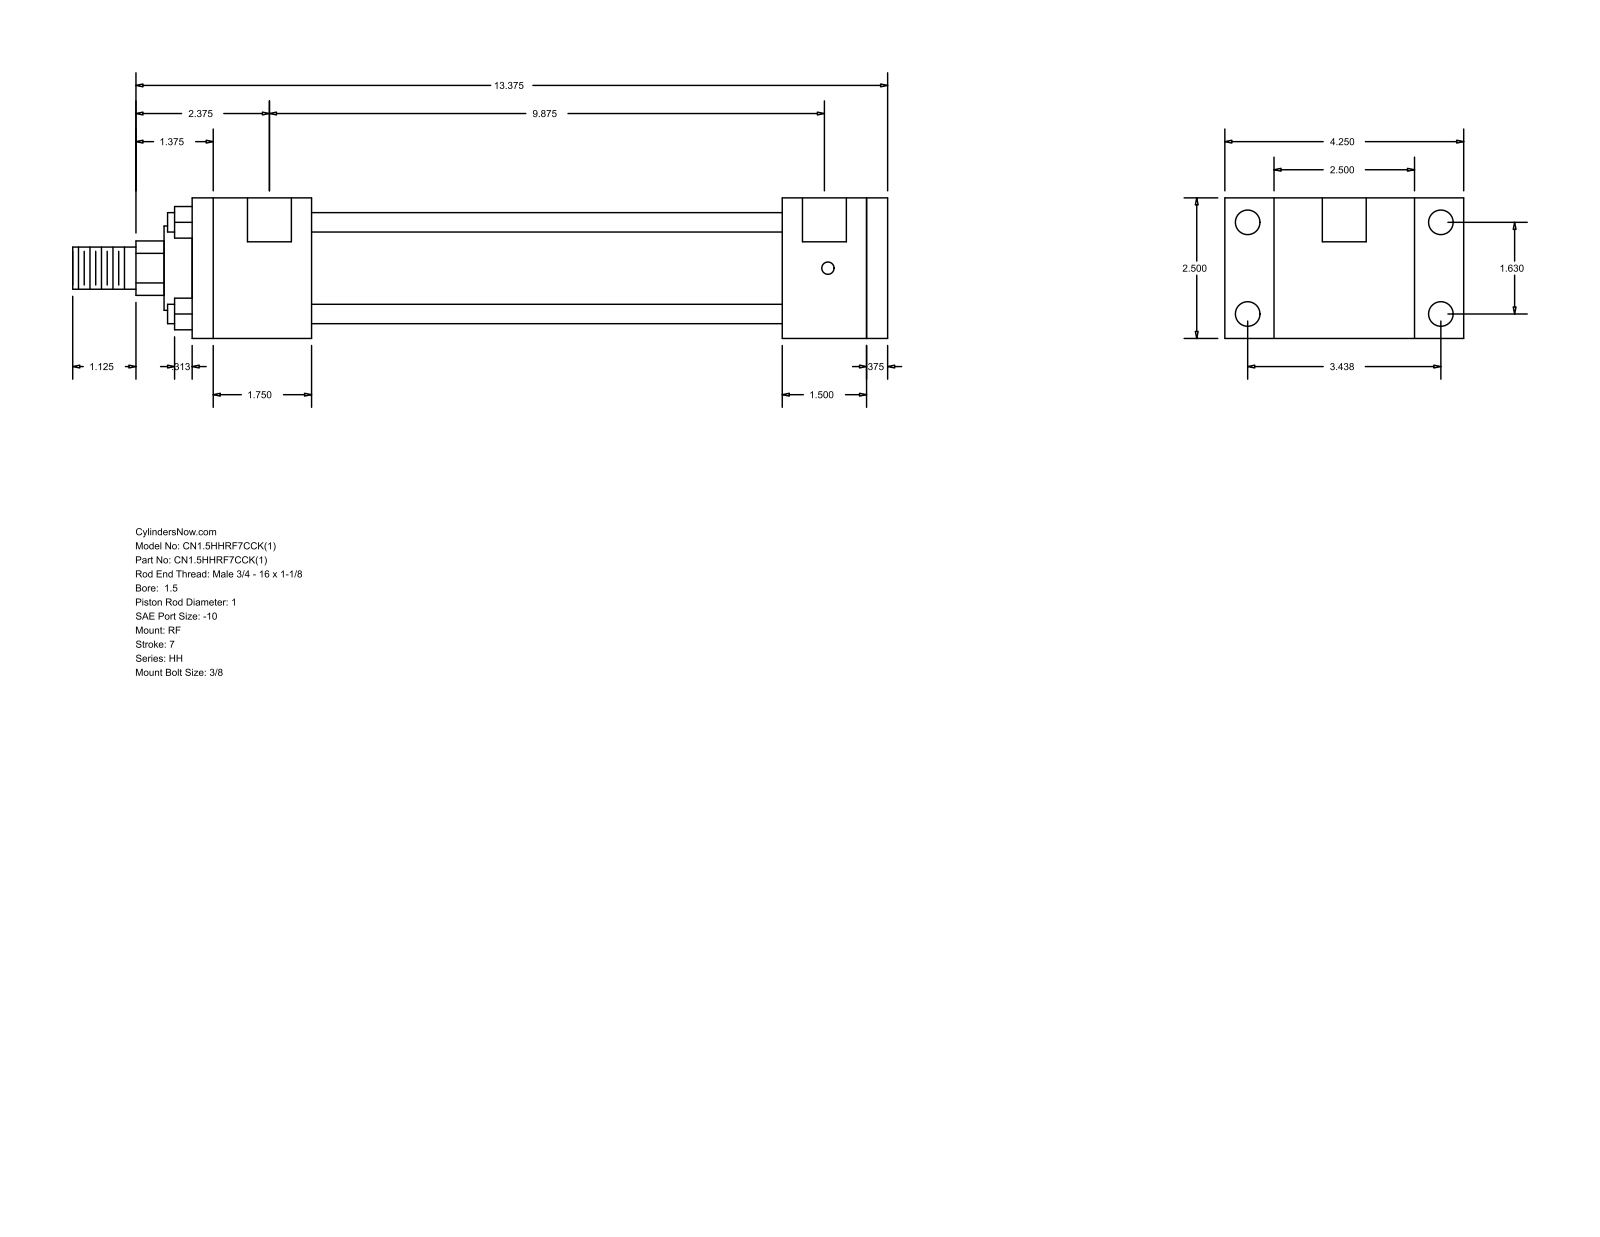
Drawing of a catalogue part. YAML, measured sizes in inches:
part_name: "HH_RF__0150_1"
step_written_by: "GSSL Pune (CONFIG_CONTROL_DESIGN)"
units: inches
bodies: {solids: 0, faces: 92, planar: 64, cylindrical: 28, other: 0}
overall_size: [14.5, 4.25, 2.5]
round_holes:
  - {diameter: 0.219, count: 4}
  - {diameter: 0.438, count: 4}
  - {diameter: 0.781, count: 2}
round_bosses_or_shafts:
  - {diameter: 0.345, count: 4}
  - {diameter: 1.75, count: 1}
  - {diameter: 1.5, count: 1}
  - {diameter: 1, count: 1}
  - {diameter: 0.75, count: 1}
partial_cylinders:
  - {radius: 0.484, count: 1}
face_to_face_distances: [2.5, 0.375, 1.5, 8.375, 9.875, 10.25, 1.875, 2.125, 10.5, 12]
hole_center_spacings: [0.063, 1.63, 3.438, 3.805, 9.937, 10, 9.875]
